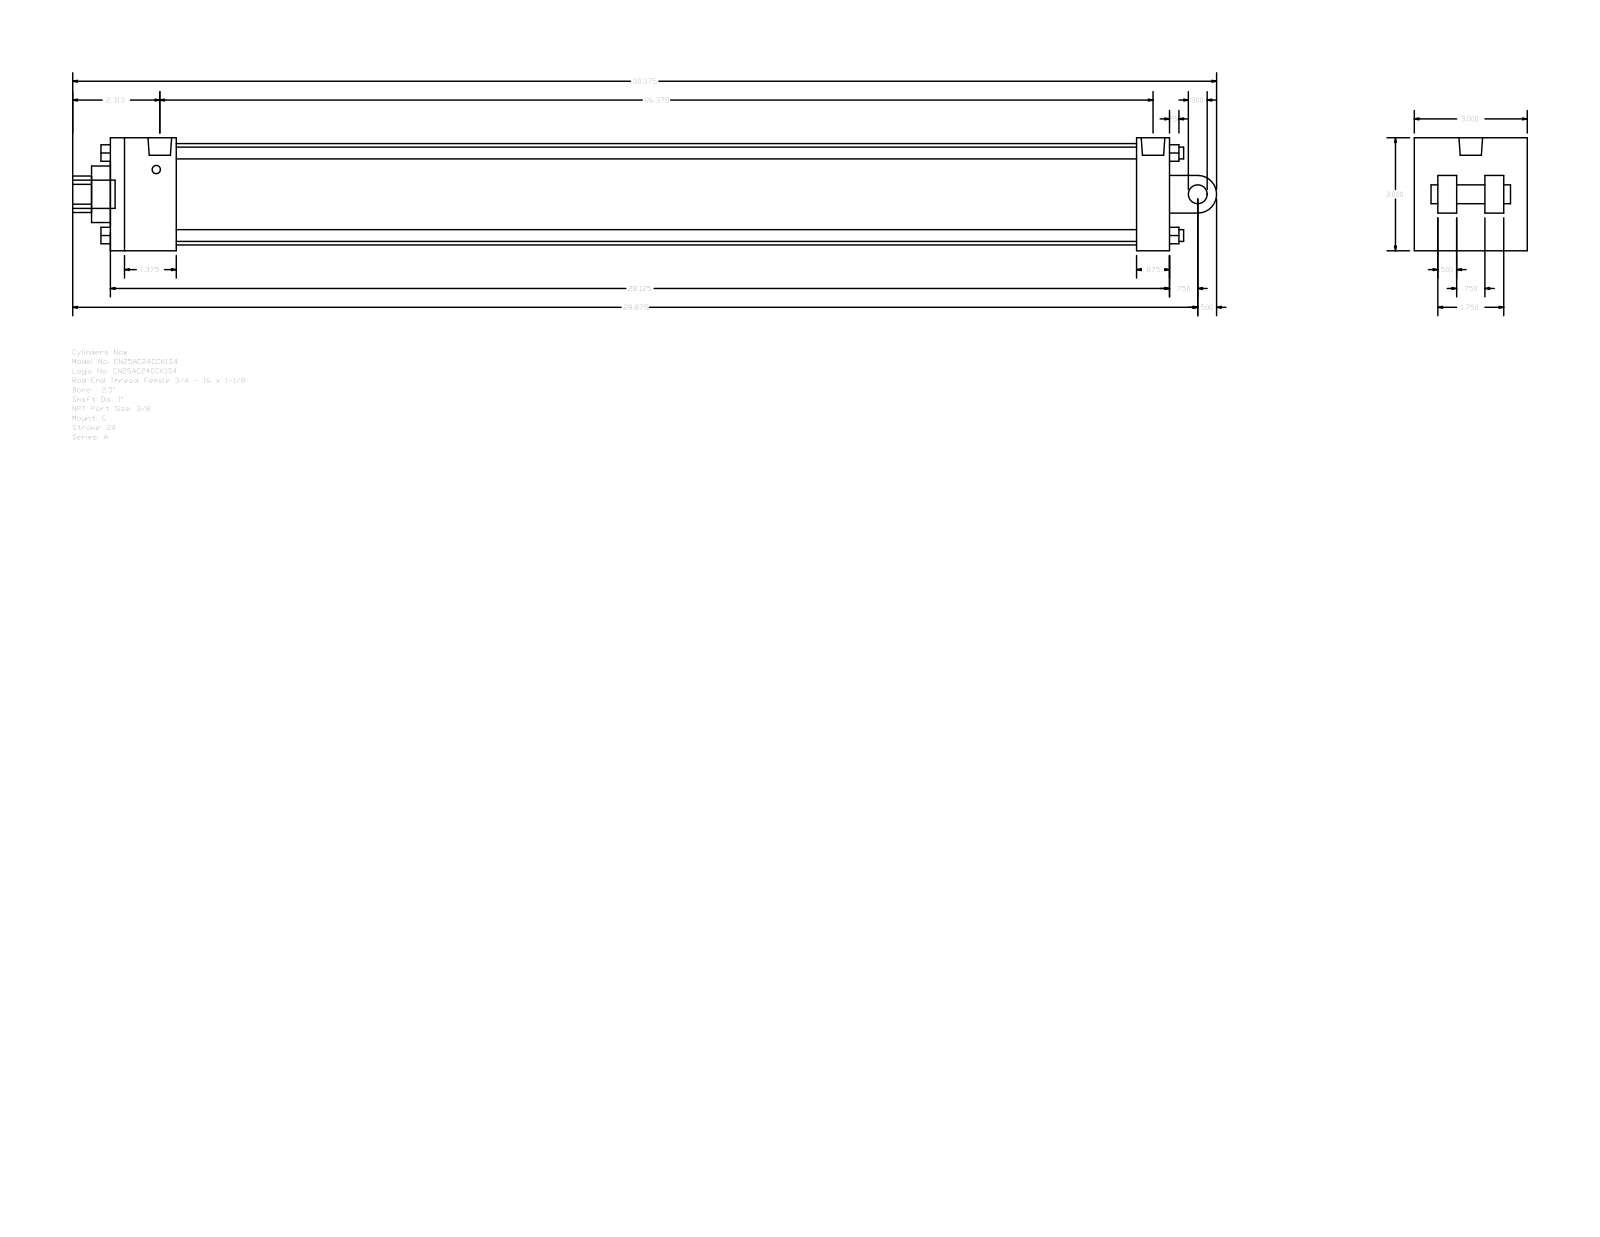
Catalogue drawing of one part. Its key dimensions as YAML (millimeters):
part_name: "A_C__0250_1"
step_written_by: "GSSL Pune (CONFIG_CONTROL_DESIGN)"
units: millimeters
bodies: {solids: 0, faces: 135, planar: 102, cylindrical: 33, other: 0}
overall_size: [771.52, 76.2, 76.2]
round_holes:
  - {diameter: 5.56, count: 2}
  - {diameter: 15.93, count: 1}
  - {diameter: 25.4, count: 1}
  - {diameter: 38.1, count: 1}
  - {diameter: 68.33, count: 1}
round_bosses_or_shafts:
  - {diameter: 7.94, count: 4}
  - {diameter: 5.56, count: 2}
  - {diameter: 19.05, count: 1}
  - {diameter: 15.93, count: 1}
  - {diameter: 12.7, count: 1}
partial_cylinders:
  - {radius: 12.29, count: 1}
  - {radius: 12.7, count: 1}
face_to_face_distances: [76.2, 714.37, 12.7, 44.45, 692.15, 647.7, 669.92, 22.22, 15.87, 25.4]
hole_center_spacings: [2.38]
